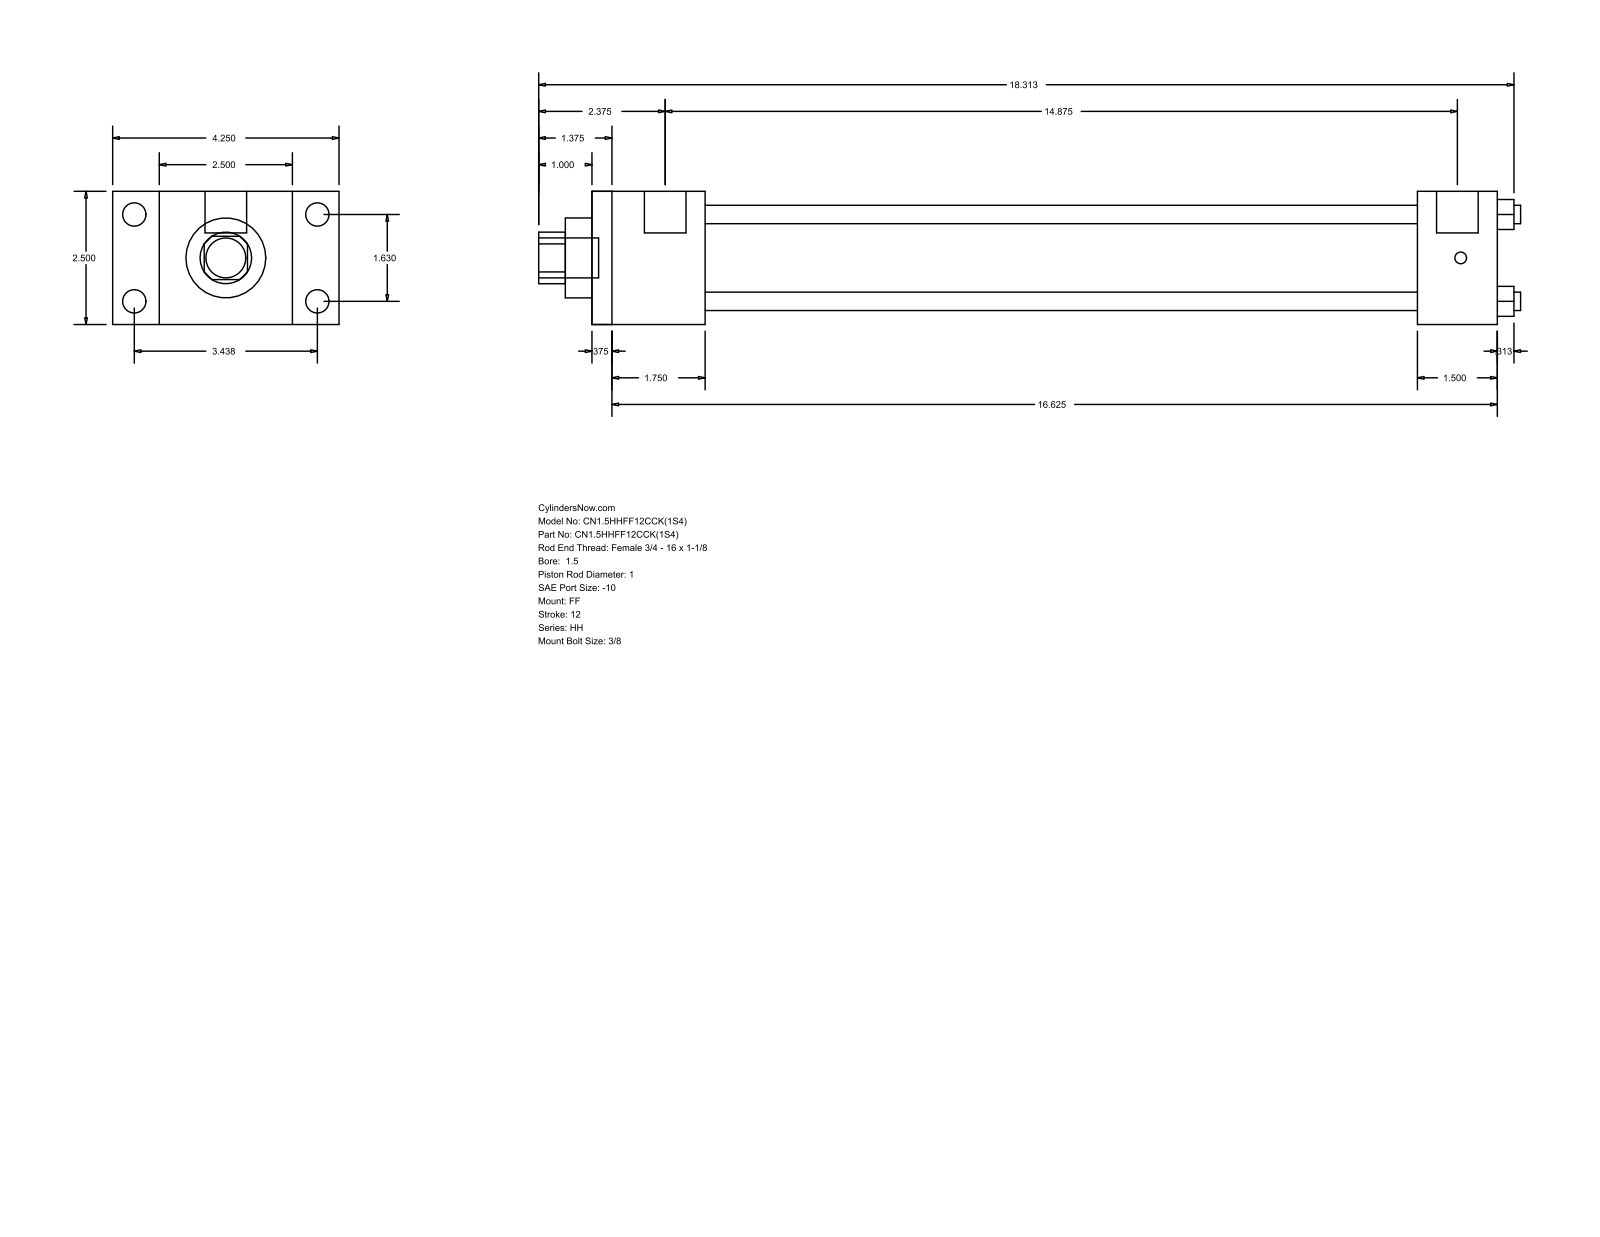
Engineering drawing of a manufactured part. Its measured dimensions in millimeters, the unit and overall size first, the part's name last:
Units: millimetres
Overall size (bounding box): 468.31 × 107.95 × 63.5
Round holes (diameter × count): ⌀8.76 ×4, ⌀25.4 ×1, ⌀38.1 ×1, ⌀44.45 ×1
Round bosses / shafts (diameter × count): ⌀11.13 ×4, ⌀5.56 ×4, ⌀19.84 ×2, ⌀19.05 ×1
Partial cylindrical surfaces — rounded edges, fillets, slot ends (radius × count): R12.29 ×1
Main face-to-face distances: 63.5, 431.8, 9.52, 422.28, 53.98, 44.46, 377.82, 393.7, 384.18, 339.72
Hole centre spacings: 29.27, 41.4, 58.55
Bodies: 0 solids, 92 faces (64 planar, 28 cylindrical, 0 other)
Part name (STEP PRODUCT): HH_FF__0150_1
STEP written by: GSSL Pune (CONFIG_CONTROL_DESIGN)
